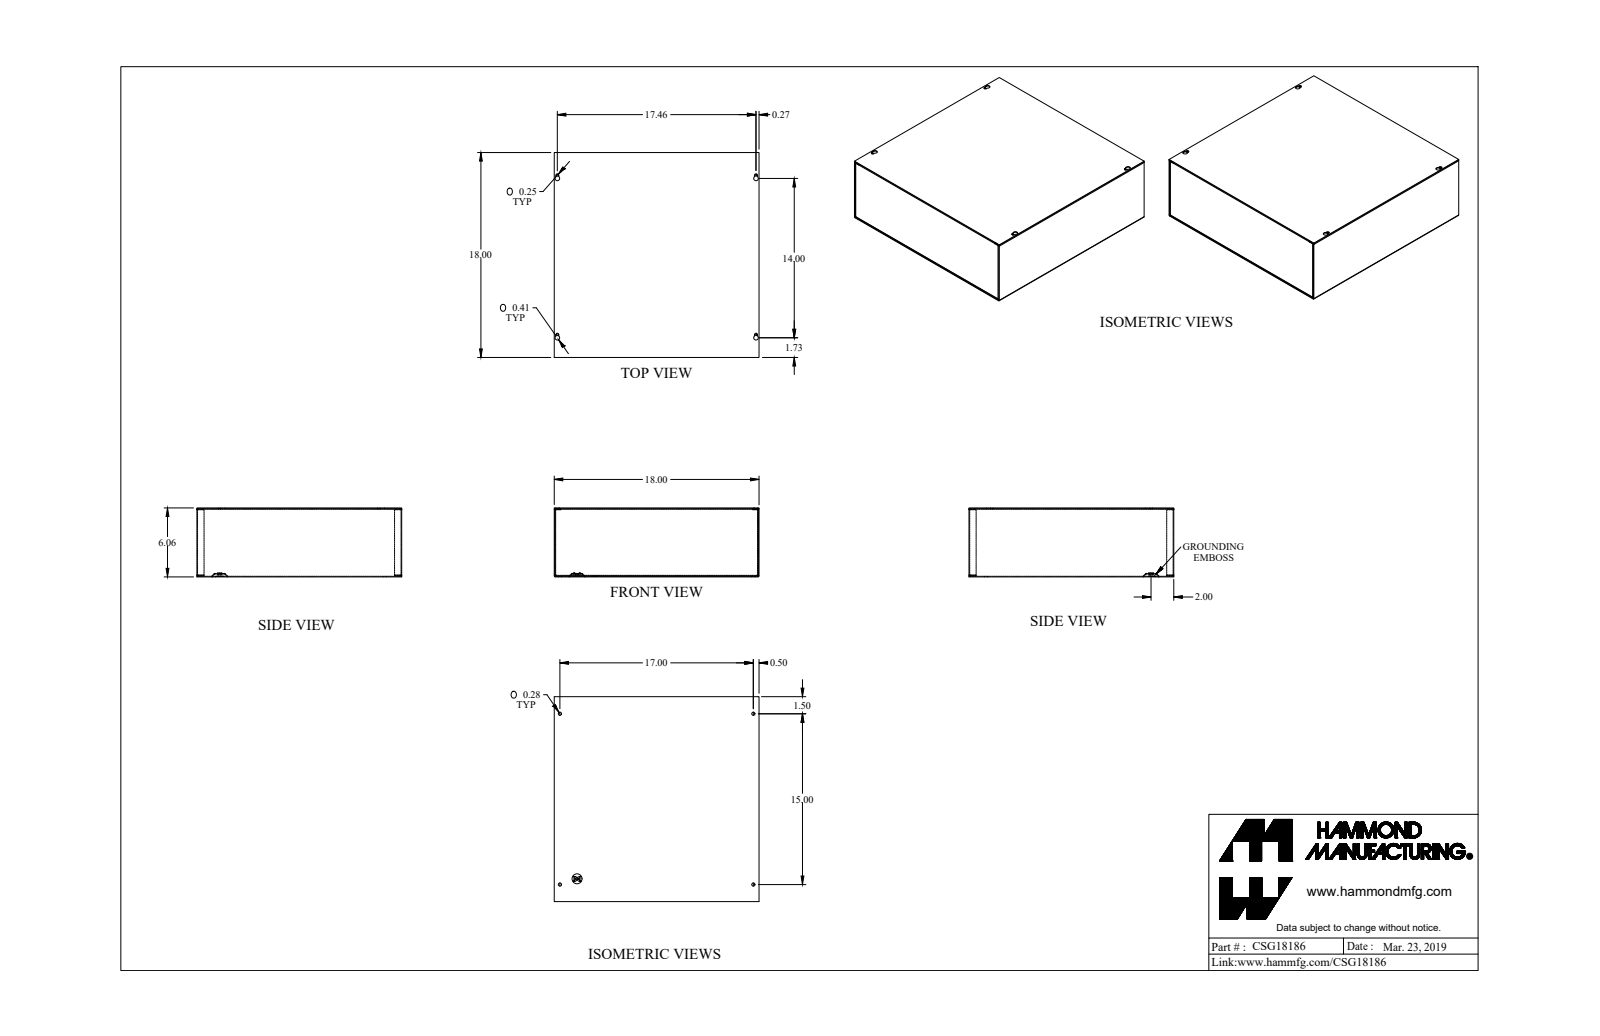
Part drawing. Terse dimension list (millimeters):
name: CSG18186_Default
written by: SolidWorks 2019 (CONFIG_CONTROL_DESIGN)
unit: mm
bodies: 4 solids, 205 faces (125 planar, 72 cylindrical, 8 other)
size: 457.2 × 457.2 × 153.8
volume: 1 058 000 mm³; area: 1 472 000 mm²
holes: 5× ⌀4.3, 4× ⌀7.1, 1× ⌀12.7
bosses: 1× ⌀12.5, 1× ⌀7.2
rounds: 12× R0.7, 12× R2.2, 8× R1.4, 4× R3.2, 4× R5.2
face distances: 1.4, 152.4, 455.8, 151, 153.8, 457.2, 454.3, 2, 148.9, 150.4
hole spacings: 14, 368.4, 437.8, 572, 355.6, 381, 431.8, 443.5
